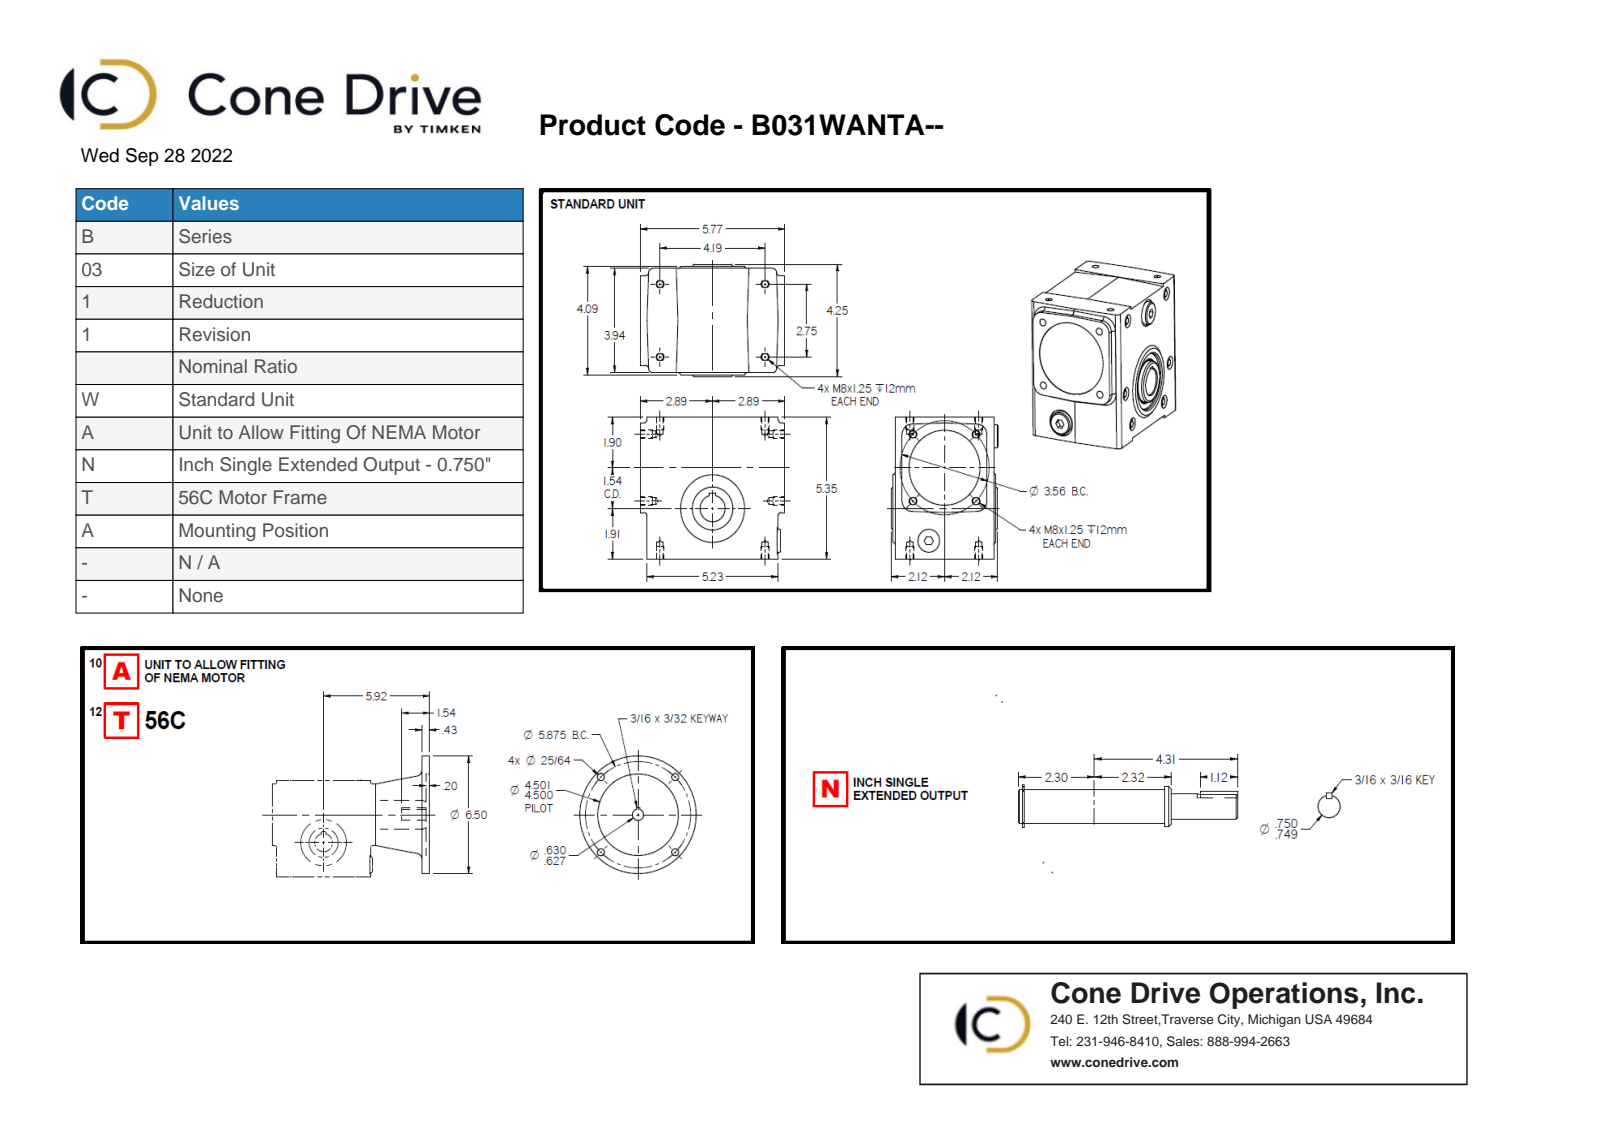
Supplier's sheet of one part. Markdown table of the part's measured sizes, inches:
| quantity | value |
| --- | --- |
| part name | B031110.WANTA; B03-1-CP; B03-0N-CP; B03-04T-CP |
| STEP written by | Solid Edge (AUTOMOTIVE_DESIGN) |
| units | inches |
| bodies | 13 solids, 576 faces (300 planar, 148 cylindrical, 128 other) |
| overall size | 8.804 × 7.56 × 6.72 |
| volume | 122.4 in³ |
| surface area | 488.8 in² |
| round holes (diameter × count) | 0.492 × 6, 0.262 × 4, 0.272 × 4, 0.346 × 4, 0.394 × 4, 0.078 × 2, 1.024 × 2, 0.5 × 1, 0.628 × 1, 0.748 × 1, 1 × 1, 1 × 1 |
| round bosses / shafts (diameter × count) | 0.394 × 6, 0.236 × 6, 0.506 × 4, 0.02 × 3, 1.572 × 2, 0.866 × 2, 6.5 × 1, 2.804 × 1 |
| partial cylindrical surfaces (radius × count) | 0.125 × 12, 0.01 × 4, 0.157 × 4, 0.295 × 4, 0.394 × 4, 0.008 × 2, 0.024 × 2, 0.1 × 2 |
| main face-to-face distances | 3.935, 3.031, 2.606, 0.425, 0.669, 5.102, 5.348, 0.571, 0.098, 5.673 |
| hole center spacings | 3.436, 1.156, 1.781, 2.52, 2.937, 4.154, 4.719, 0.571 |
